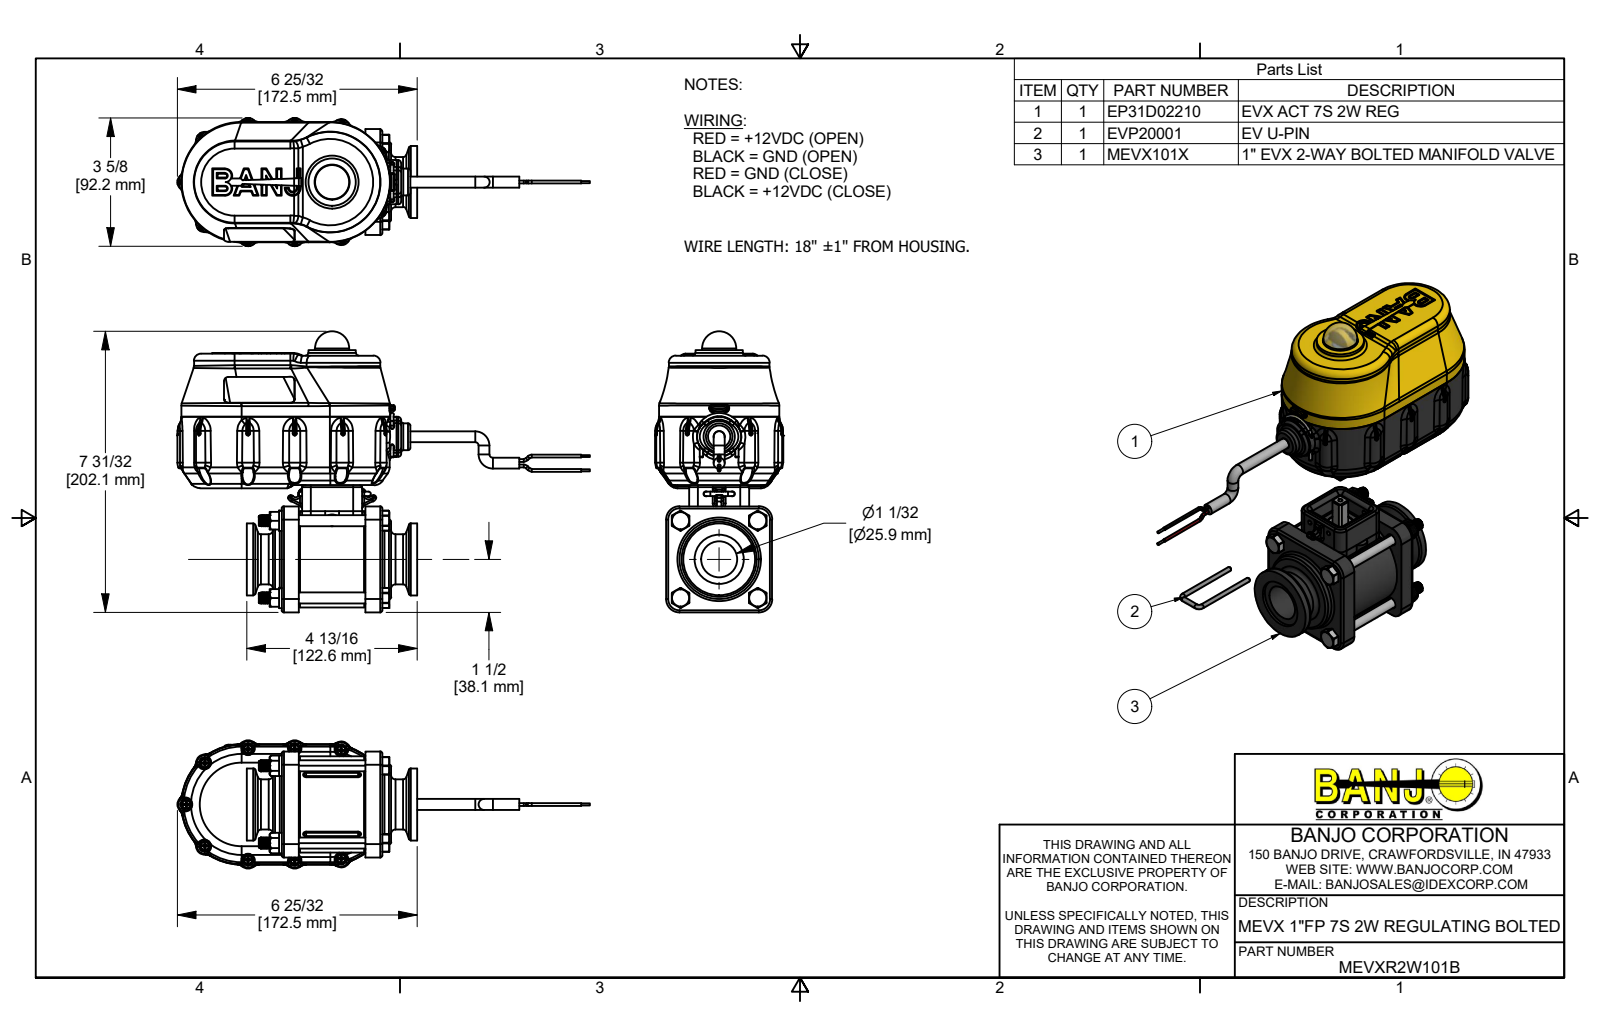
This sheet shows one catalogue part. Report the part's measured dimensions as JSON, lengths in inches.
{"part_name": "MEVXR2W101B; EP31D02210; 91400A119; 95584A200 (+8 more)", "step_written_by": "Autodesk Inventor 2019 (AUTOMOTIVE_DESIGN)", "units": "inches", "bodies": {"solids": 95, "faces": 12585, "planar": 3496, "cylindrical": 3419, "other": 5670}, "overall_size": [11.685, 7.957, 3.63], "volume_in3": 51.14, "surface_area_in2": 582.1, "round_holes": [[0.15, 13], [0.095, 11], [0.107, 4], [0.126, 4], [0.136, 4], [0.17, 4], [0.252, 4], [0.322, 4], [0.35, 4], [0.135, 3], [1.02, 3], [0.089, 2]], "round_bosses_or_shafts": [[0.268, 60], [0.25, 17], [0.14, 11], [0.108, 11], [0.085, 11], [0.08, 10], [0.313, 5], [0.583, 4]], "partial_cylinders_radius": [[0.04, 147], [0.02, 83], [0.01, 56], [0.06, 46], [0.005, 43], [0.03, 32], [0.08, 28], [0.1, 22]], "face_to_face_distances": [0.1, 2.565, 1.685, 0.78, 2.465, 0.055, 0.48, 0.165, 0.88, 0.035], "hole_center_spacings": [1.283, 1.547, 2.188, 1.662, 1.891, 2.73, 2.967, 3.294]}
